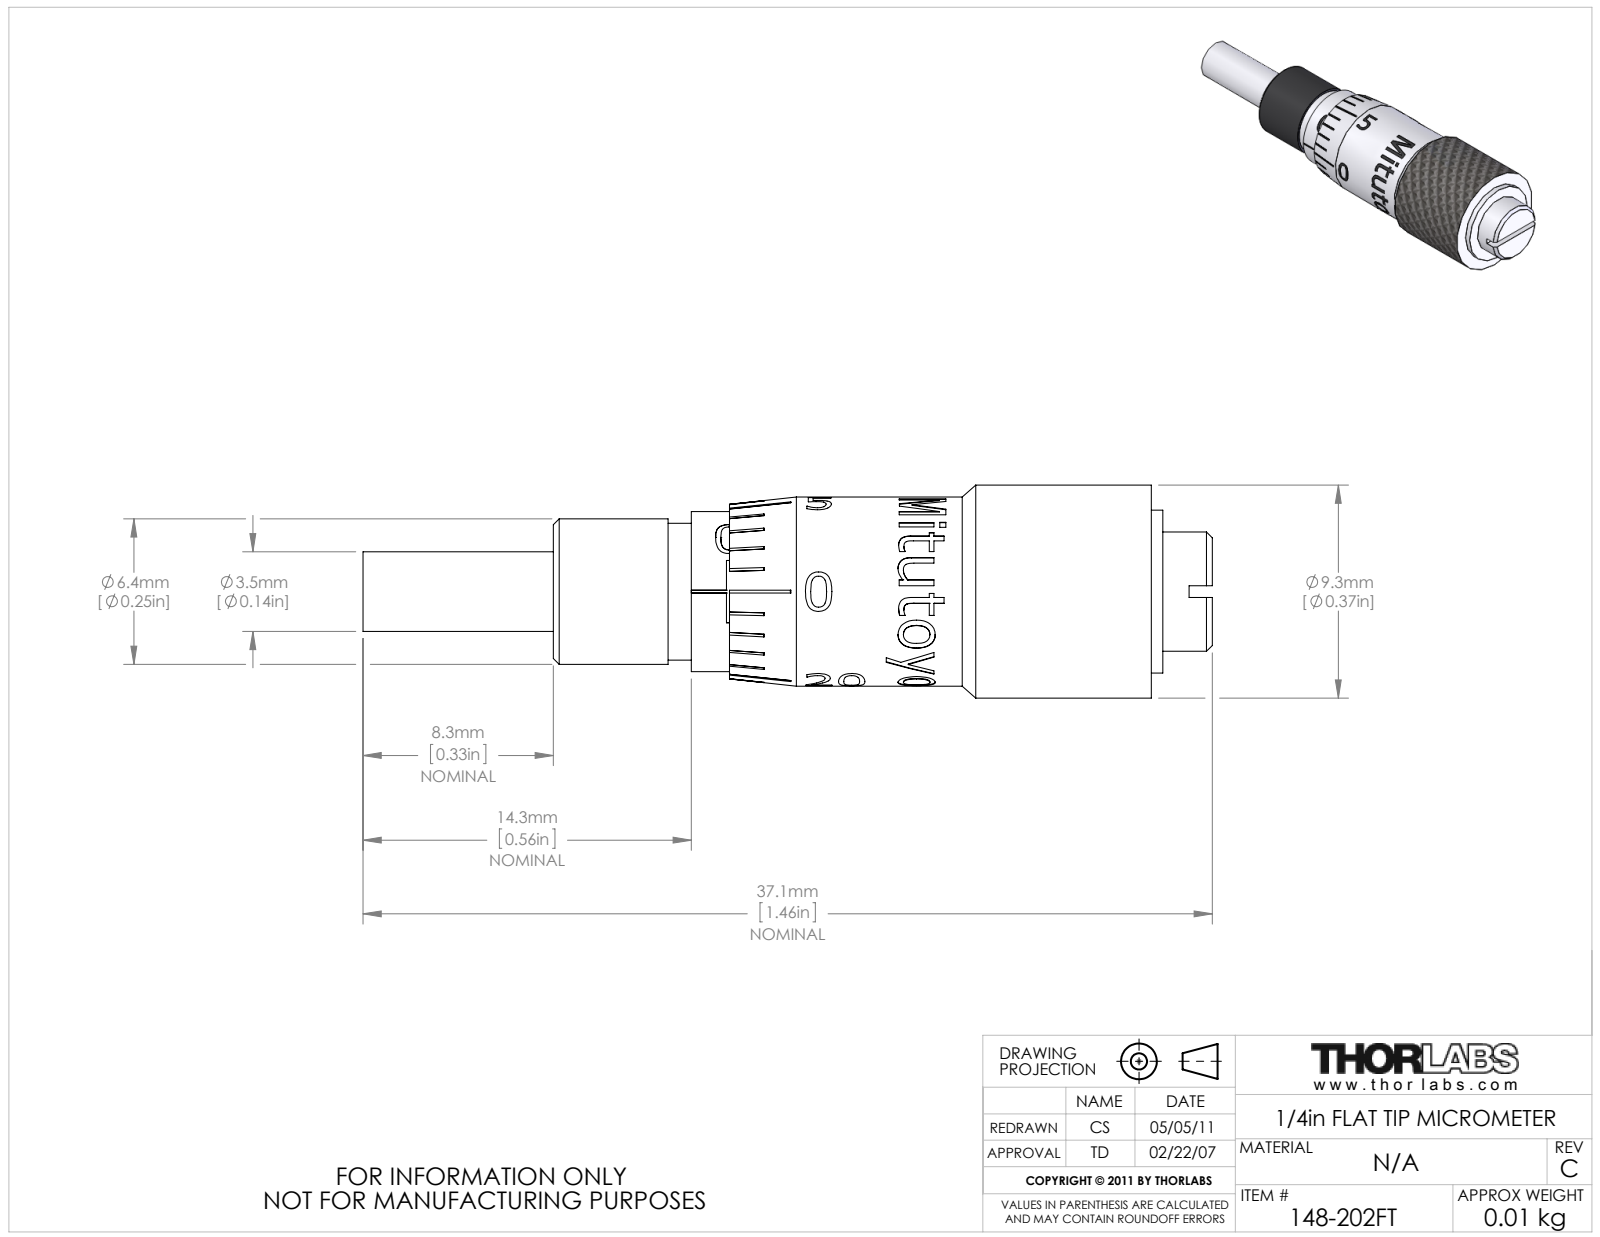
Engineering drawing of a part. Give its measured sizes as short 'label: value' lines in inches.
name: 16384-E0W
written by: SolidWorks 2012 (AUTOMOTIVE_DESIGN)
unit: in
bodies: 2 solids, 388 faces (232 planar, 53 cylindrical, 103 other)
size: 1.46 × 0.366 × 0.366
volume: 0.102 in³; area: 2.709 in²
holes: 1× ⌀0.138, 1× ⌀0.175, 1× ⌀0.285
bosses: 1× ⌀0.366, 1× ⌀0.325, 1× ⌀0.28, 1× ⌀0.275, 1× ⌀0.255, 1× ⌀0.25, 1× ⌀0.235, 1× ⌀0.205
rounds: 1× R0.137, 1× R0.161
face distances: 0.545, 0.02, 0.565, 1.047, 1.028, 0.482, 0.085, 0.65, 0.105, 1.132
